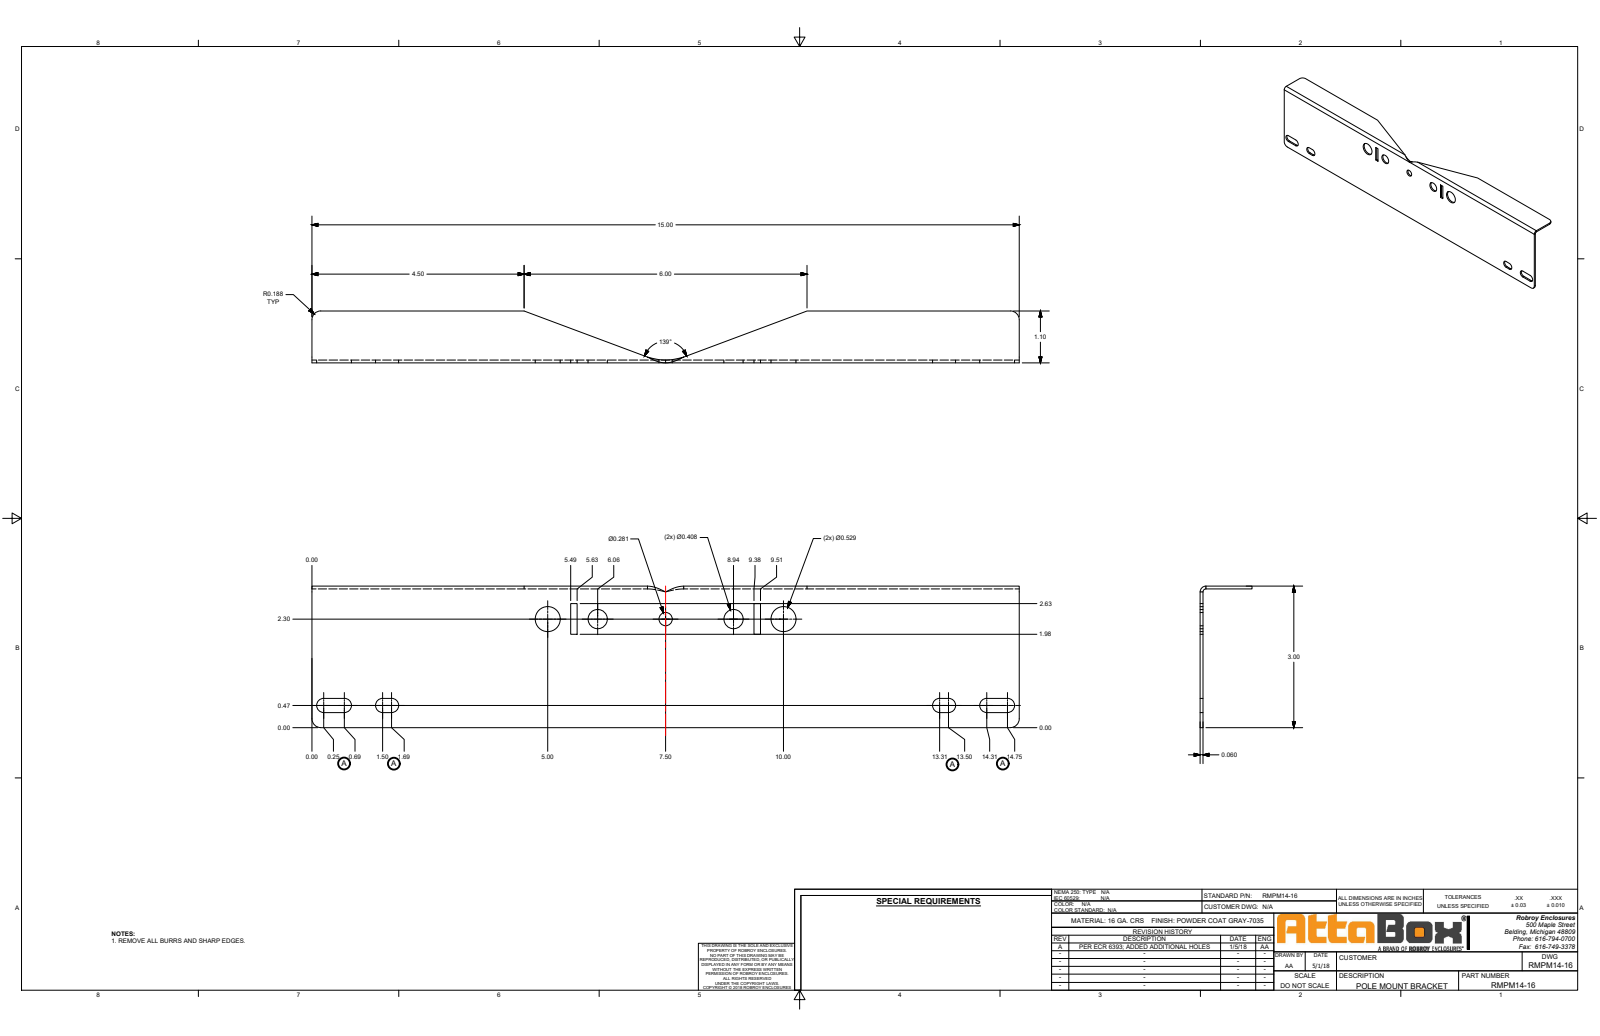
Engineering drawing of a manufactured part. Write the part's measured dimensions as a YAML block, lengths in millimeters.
part_name: "PM14-16"
step_written_by: "SolidWorks 2019 (AUTOMOTIVE_DESIGN)"
units: millimeters
bodies: {solids: 1, faces: 56, planar: 33, cylindrical: 21, other: 2}
overall_size: [381, 76.2, 27.9]
volume: 54090
surface_area: 73100
round_holes:
  - {diameter: 10.4, count: 2}
  - {diameter: 13.4, count: 2}
  - {diameter: 7.1, count: 1}
partial_cylinders:
  - {radius: 3.8, count: 8}
  - {radius: 4.7, count: 2}
  - {radius: 4.8, count: 2}
  - {radius: 1.6, count: 1}
  - {radius: 3.1, count: 1}
face_to_face_distances: [1.5, 74.7, 76.2, 26.4, 27.9, 381, 142.9, 238.1, 139.4, 241.6]
hole_center_spacings: [26.9, 36.6, 63.5, 100.1, 73.2, 127]
